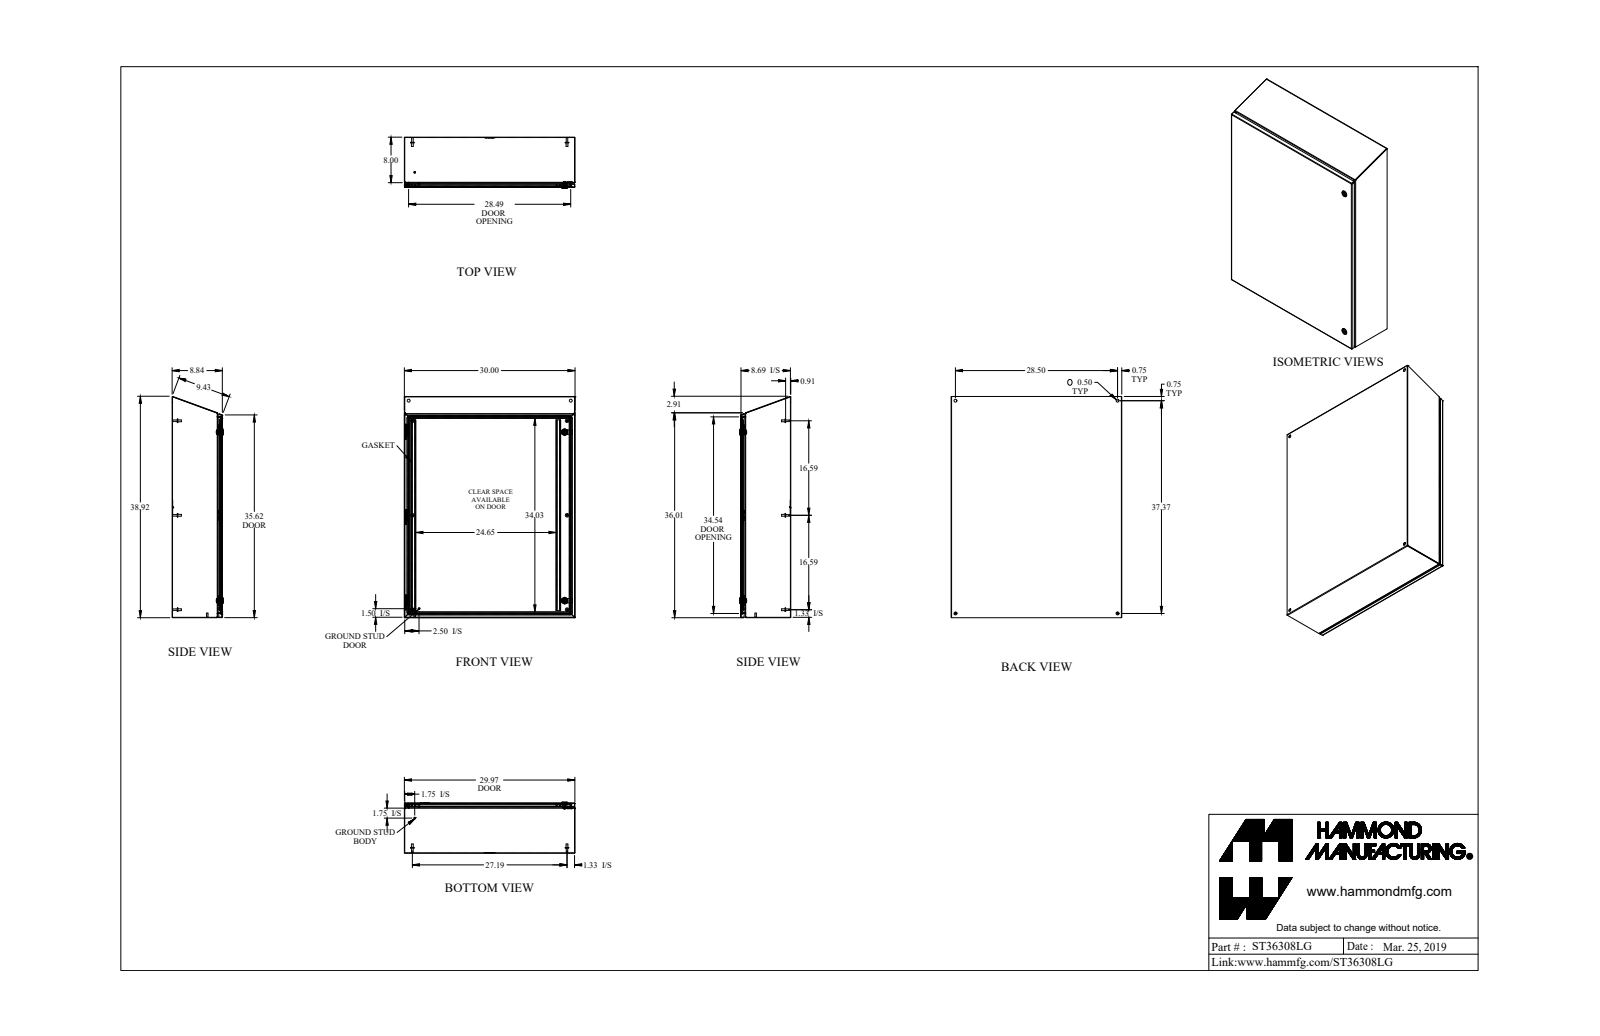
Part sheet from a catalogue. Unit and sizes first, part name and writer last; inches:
Units: inches
Overall size (bounding box): 38.872 × 30 × 8.997
Round holes (diameter × count): ⌀0.5 ×4, ⌀0.172 ×2, ⌀0.232 ×2, ⌀0.242 ×2, ⌀0.625 ×2, ⌀0.785 ×2, ⌀0.24 ×1
Round bosses / shafts (diameter × count): ⌀0.625 ×6, ⌀0.313 ×6, ⌀0.27 ×6, ⌀1.1 ×2, ⌀0.525 ×2, ⌀0.356 ×2, ⌀0.292 ×2, ⌀0.281 ×2
Partial cylindrical surfaces — rounded edges, fillets, slot ends (radius × count): R0.036 ×18, R0.108 ×18, R0.043 ×12, R0.081 ×12, R0.006 ×6, R0.062 ×6, R0.188 ×5, R0.125 ×4
Main face-to-face distances: 0.072, 8.765, 8.693, 8.837, 29.928, 29.856, 30, 7.928, 0.837, 0.909
Hole centre spacings: 28.5, 37.372, 46.999, 2.494, 5.62, 27.519, 27.976, 29.604
Volume: 275.6 in³ · Surface area: 7 734 in²
Bodies: 35 solids, 900 faces (438 planar, 290 cylindrical, 172 other)
Part name (STEP PRODUCT): ST36308LG
STEP written by: SolidWorks 2018 (AUTOMOTIVE_DESIGN)
